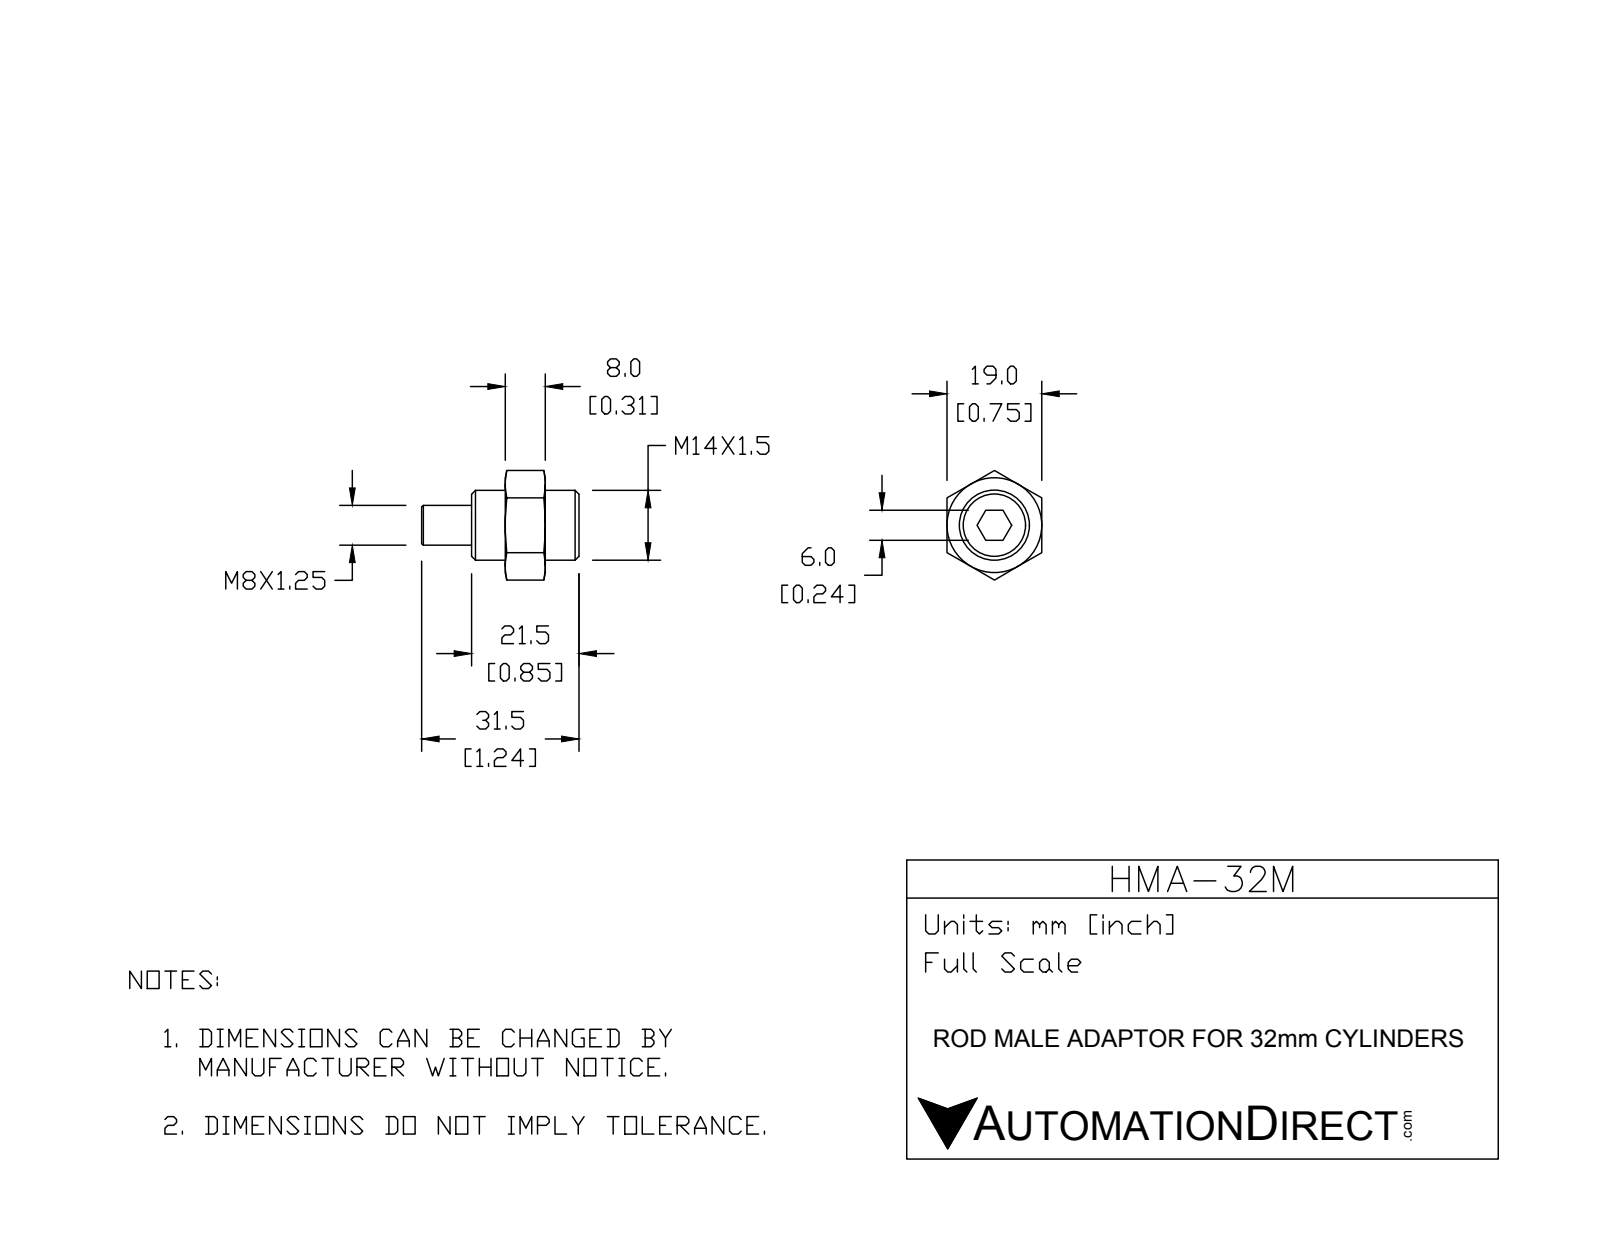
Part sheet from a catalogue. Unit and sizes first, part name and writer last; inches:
Units: inches
Overall size (bounding box): 1.24 × 0.864 × 0.748
Round holes (diameter × count): ⌀0.551 ×1
Round bosses / shafts (diameter × count): ⌀0.315 ×1
Main face-to-face distances: 0.748, 0.266, 0.581, 0.315, 0.846, 0.236, 1.24, 0.974, 0.659, 0.394
Volume: 0.298 in³ · Surface area: 4.273 in²
Bodies: 2 solids, 44 faces (18 planar, 6 cylindrical, 20 other)
Part name (STEP PRODUCT): HMA-32M
STEP written by: SolidWorks 2015 (CONFIG_CONTROL_DESIGN)
